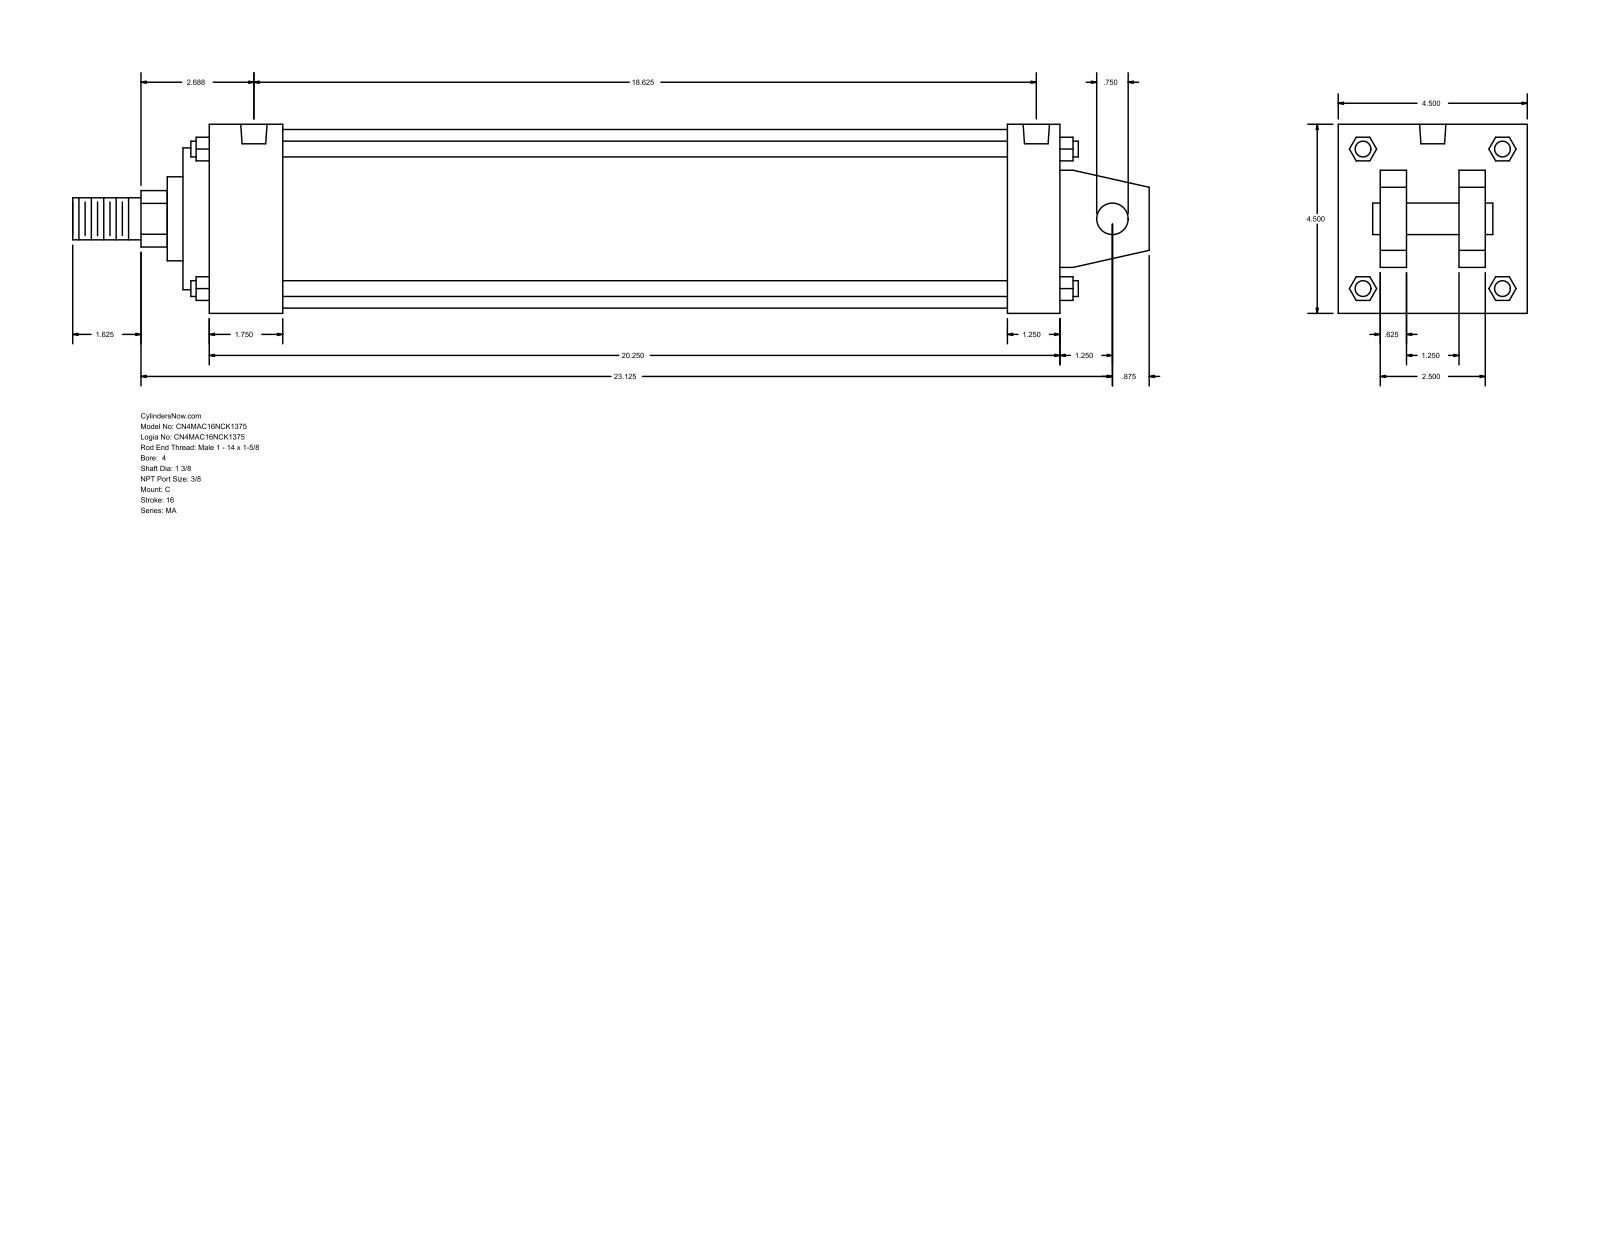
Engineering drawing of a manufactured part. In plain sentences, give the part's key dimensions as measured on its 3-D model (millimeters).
The part is named "MA_C__0400_1.375". Its 3-D file was written by "GSSL Pune (CONFIG_CONTROL_DESIGN)". It is 0 solids with 141 faces: 109 planar, 32 cylindrical and 0 other. Overall it measures 650.88 by 114.3 by 114.3 millimeters. Round holes: 4 of diameter 11.11, 2 of diameter 15.93. Round bosses or shafts: 4 of diameter 9.53, 1 of diameter 107.95, 1 of diameter 85.72, 1 of diameter 50.8, 1 of diameter 34.92, 1 of diameter 25.4, 1 of diameter 19.05. Partial cylindrical surfaces (rounded edges, fillets, slot ends): 1 of radius 17.06. The main face-to-face distances are 114.3, 15.87, 514.35, 73.03, 41.27, 25.4, 88.9, 47.63, 530.22, 498.48. The hole center spacings are 463.55, 4.76, 4.77, 468.31, 468.32, 473.08.
